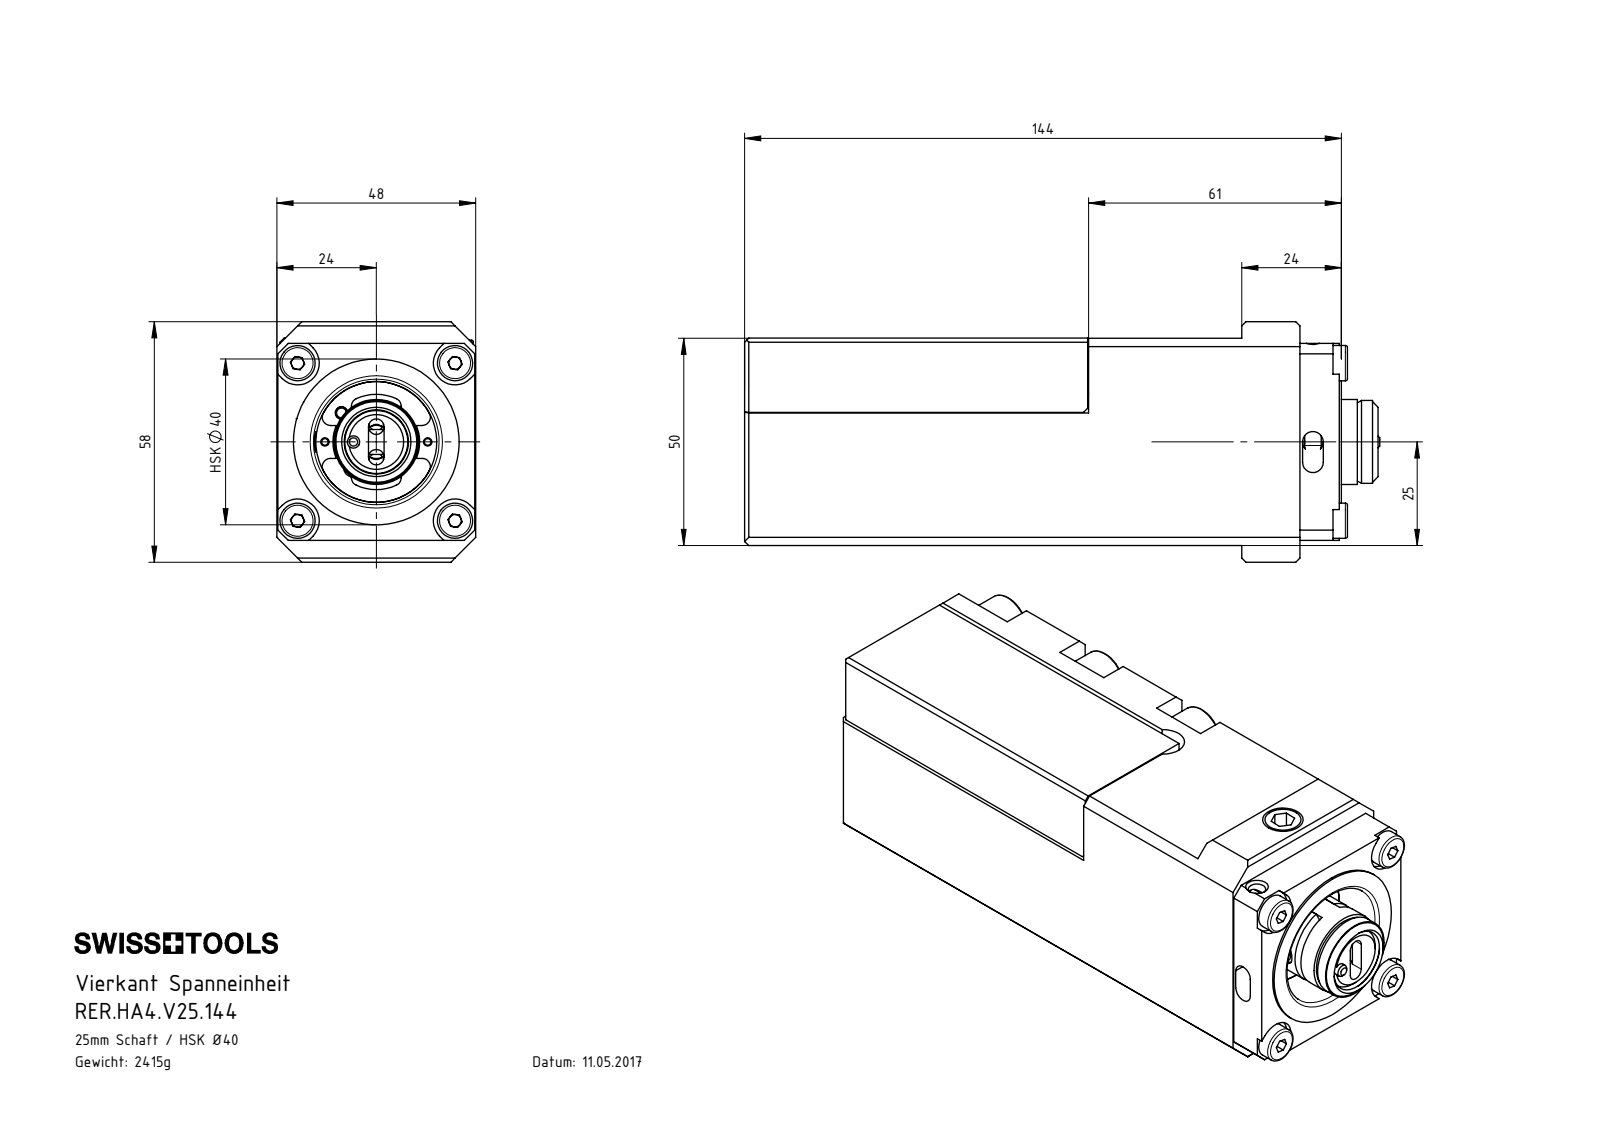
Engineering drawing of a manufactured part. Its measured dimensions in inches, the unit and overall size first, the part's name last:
Units: inches
Overall size (bounding box): 6.034 × 2.283 × 1.89
Round holes (diameter × count): ⌀0.165 ×5, ⌀0.217 ×4, ⌀0.268 ×3, ⌀0.354 ×3, ⌀0.063 ×2, ⌀0.118 ×2, ⌀0.13 ×2, ⌀0.138 ×2, ⌀0.148 ×2, ⌀0.094 ×1, ⌀0.157 ×1, ⌀0.197 ×1
Round bosses / shafts (diameter × count): ⌀0.197 ×5, ⌀0.335 ×4, ⌀0.512 ×3, ⌀0.315 ×3, ⌀1.575 ×1, ⌀1.559 ×1, ⌀1.555 ×1, ⌀1.488 ×1
Partial cylindrical surfaces — rounded edges, fillets, slot ends (radius × count): R0.039 ×8, R0.077 ×4, R0.079 ×4, R0.207 ×4, R0.295 ×3, R0.108 ×2, R0.02 ×1, R0.059 ×1
Main face-to-face distances: 1.89, 1.969, 1.97, 5.276, 1.654, 3.622, 1.859, 0.03, 0.157, 0.551
Hole centre spacings: 1.299, 0.509, 0.792, 0.961, 1.058, 1.165, 1.445, 1.496
Volume: 19.99 in³ · Surface area: 129.6 in²
Bodies: 24 solids, 709 faces (294 planar, 205 cylindrical, 210 other)
Part name (STEP PRODUCT): Dichtung; U40-HA4.001.010_A; RER-HA4.V25.140-11_A; HA4-ER1.001.000 (+8 more)
STEP written by: SolidWorks 2022 (AUTOMOTIVE_DESIGN)
